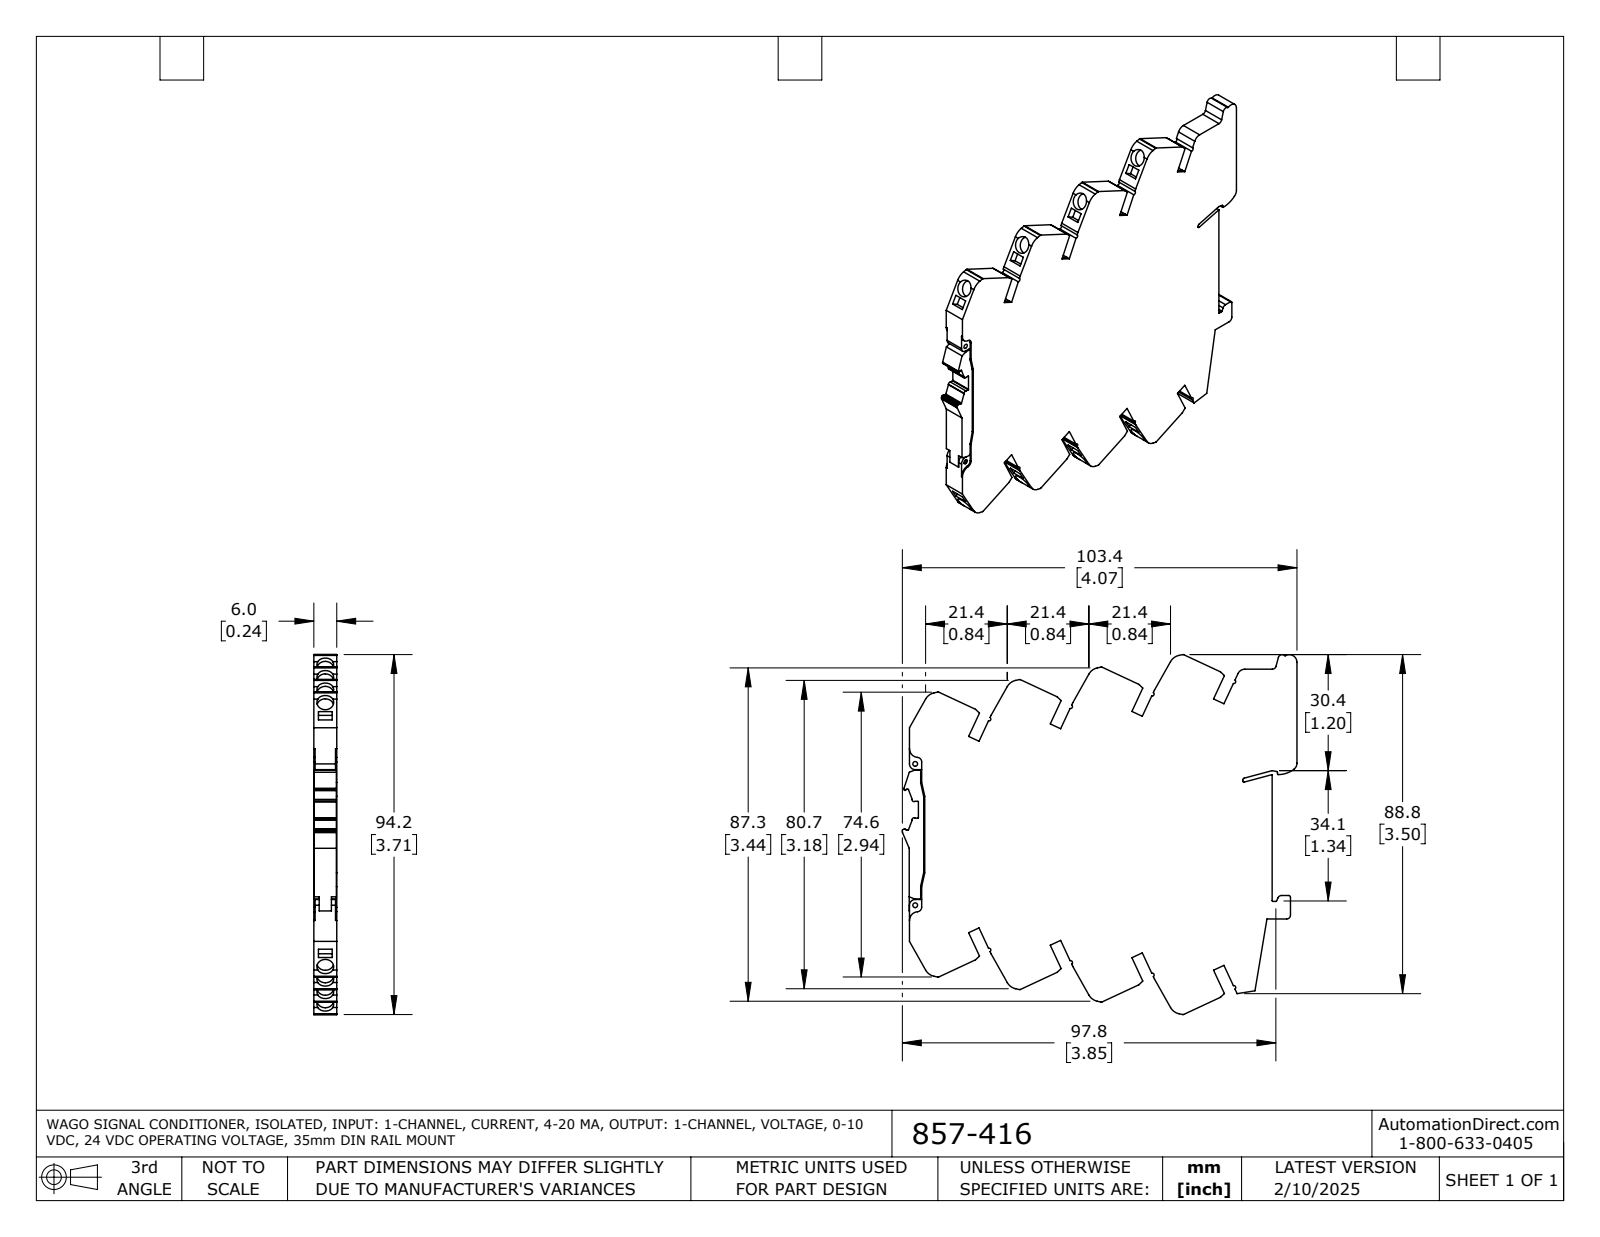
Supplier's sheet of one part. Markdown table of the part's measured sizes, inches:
| quantity | value |
| --- | --- |
| part name | 857-416 |
| STEP written by | SolidWorks 2021 (AUTOMOTIVE_DESIGN) |
| units | inches |
| bodies | 1 solid, 317 faces (219 planar, 98 cylindrical, 0 other) |
| overall size | 4.069 × 3.711 × 0.236 |
| volume | 2.681 in³ |
| surface area | 29.86 in² |
| round holes (diameter × count) | 0.173 × 8, 0.049 × 2 |
| partial cylindrical surfaces (radius × count) | 0.02 × 12, 0.008 × 11, 0.016 × 8, 0.132 × 8, 0.039 × 4, 0.012 × 3, 0.079 × 3, 0.018 × 2 |
| main face-to-face distances | 0.236, 0.708, 0.67, 0.473, 0.232, 0.472, 0.118, 0.945, 1.417, 0.256 |
| hole center spacings | 0.526, 0.525, 1.051, 1.051, 1.052, 1.457, 1.576, 1.577 |
